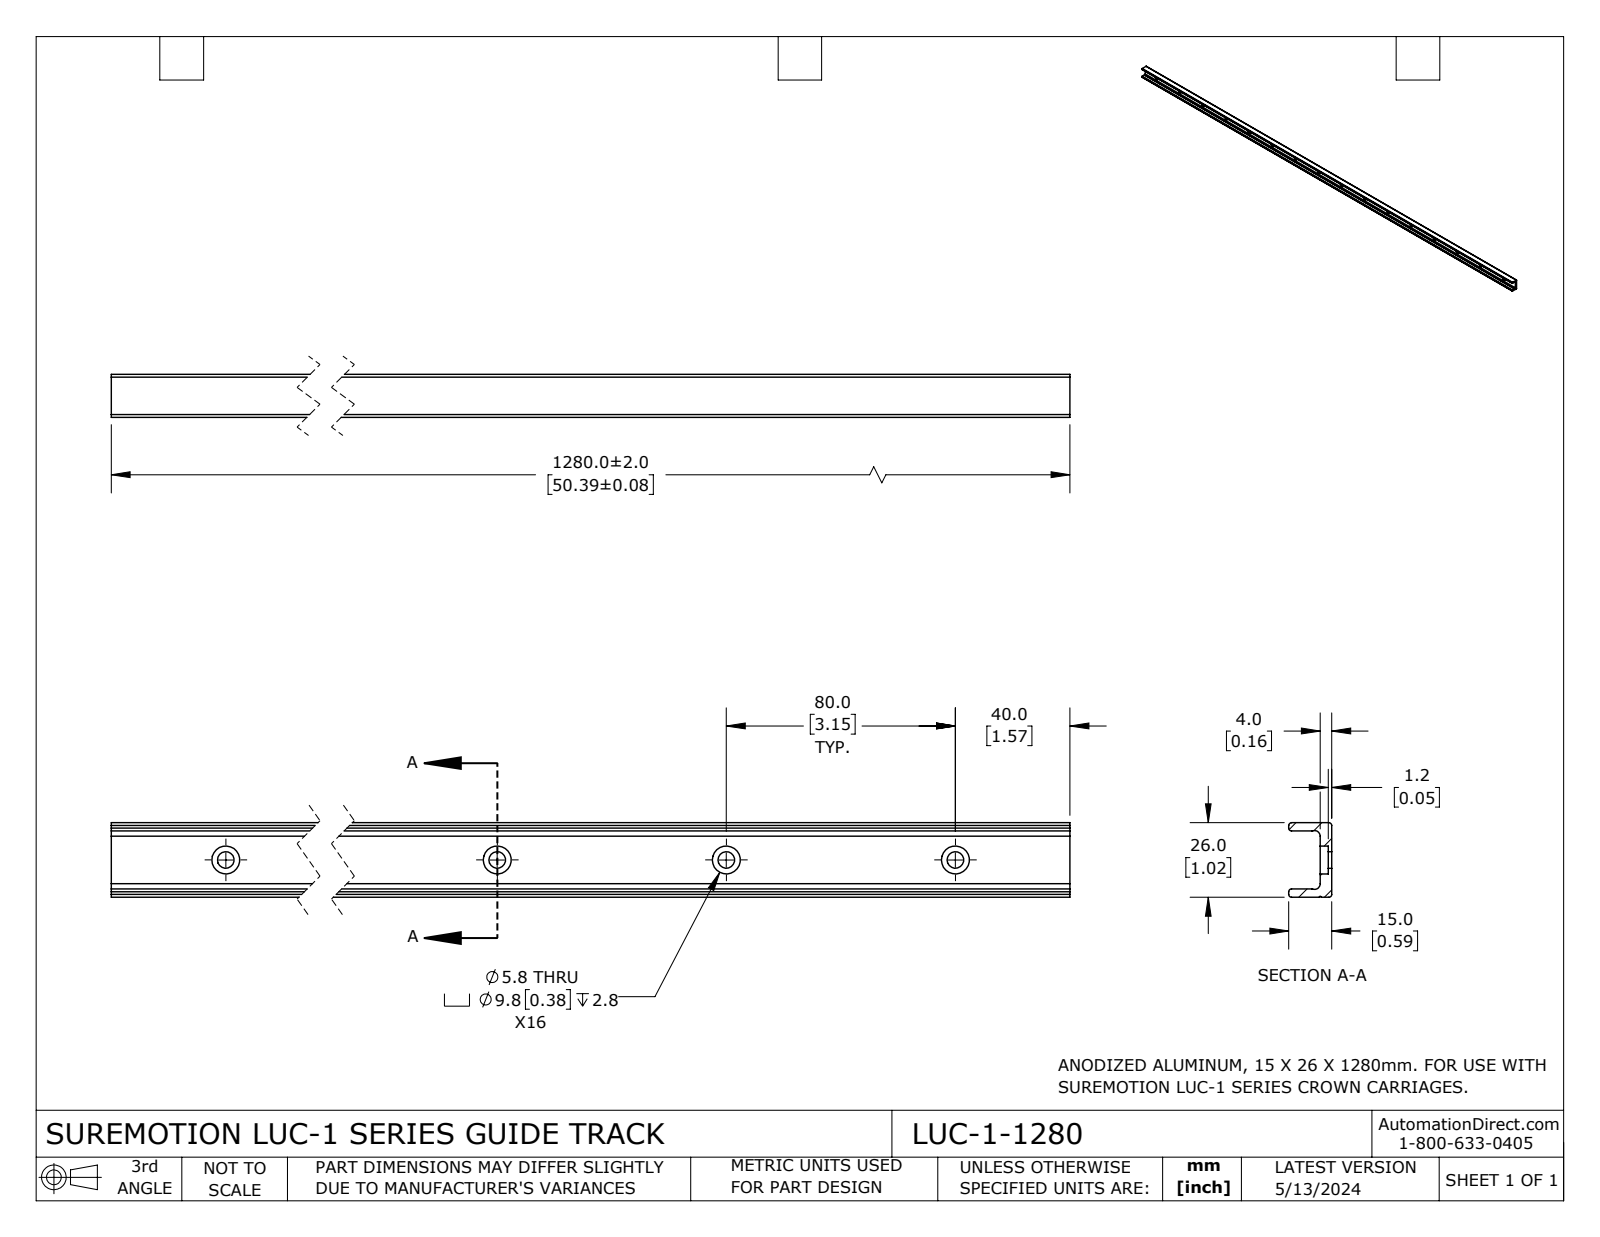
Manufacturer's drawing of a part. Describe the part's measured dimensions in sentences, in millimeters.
The part is named "LUC-1-1280". Its 3-D file was written by "SolidWorks 2023 (CONFIG_CONTROL_DESIGN)". It is 1 solid with 102 faces: 27 planar, 75 cylindrical and 0 other. Overall it measures 1280 by 26.01 by 15.01 millimeters. Its volume is 210 528 cubic millimeters and its surface area 129 855 square millimeters. Round holes: 16 of diameter 5.79, 16 of diameter 9.75. Partial cylindrical surfaces (rounded edges, fillets, slot ends): 8 of radius 0.99, 2 of radius 1.98, 1 of radius 0.33. The main face-to-face distances are 4.01, 2.9, 23.12, 26.02, 20.22, 15.02, 11.01, 1.21, 2.8, 13.81. The hole center spacings are 80, 160, 240, 320, 400, 480, 560, 640.
